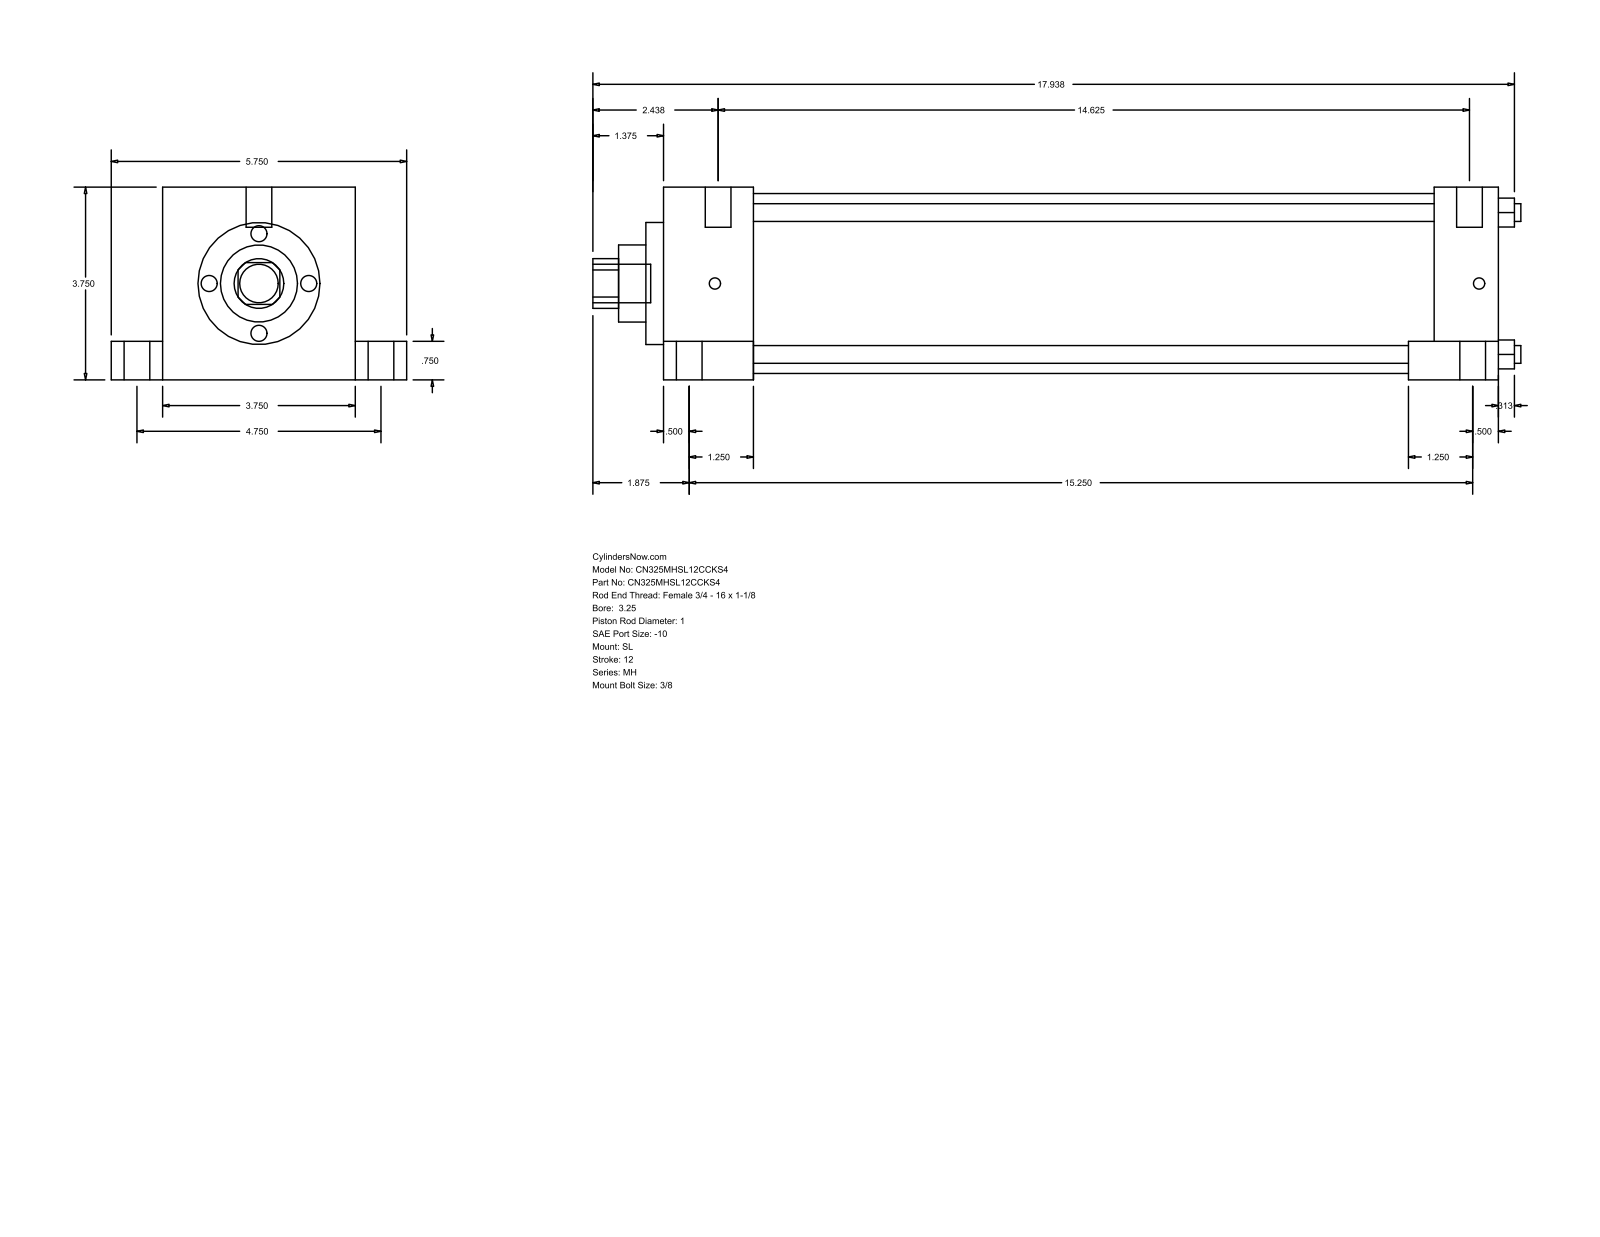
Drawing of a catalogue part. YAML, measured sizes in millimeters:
part_name: "MH_SL__0325_1"
step_written_by: "GSSL Pune (CONFIG_CONTROL_DESIGN)"
units: millimeters
bodies: {solids: 0, faces: 110, planar: 77, cylindrical: 33, other: 0}
overall_size: [458.79, 146.05, 95.25]
round_holes:
  - {diameter: 8.76, count: 4}
  - {diameter: 25.4, count: 1}
  - {diameter: 38.1, count: 1}
  - {diameter: 60.33, count: 1}
  - {diameter: 88.9, count: 1}
round_bosses_or_shafts:
  - {diameter: 12.7, count: 6}
  - {diameter: 19.05, count: 5}
  - {diameter: 5.56, count: 4}
partial_cylinders:
  - {radius: 12.29, count: 1}
face_to_face_distances: [95.24, 412.76, 44.46, 368.3, 25.41, 120.65, 19.05, 76.19, 381.01, 336.55]
hole_center_spacings: [49.57, 70.1, 99.14]
